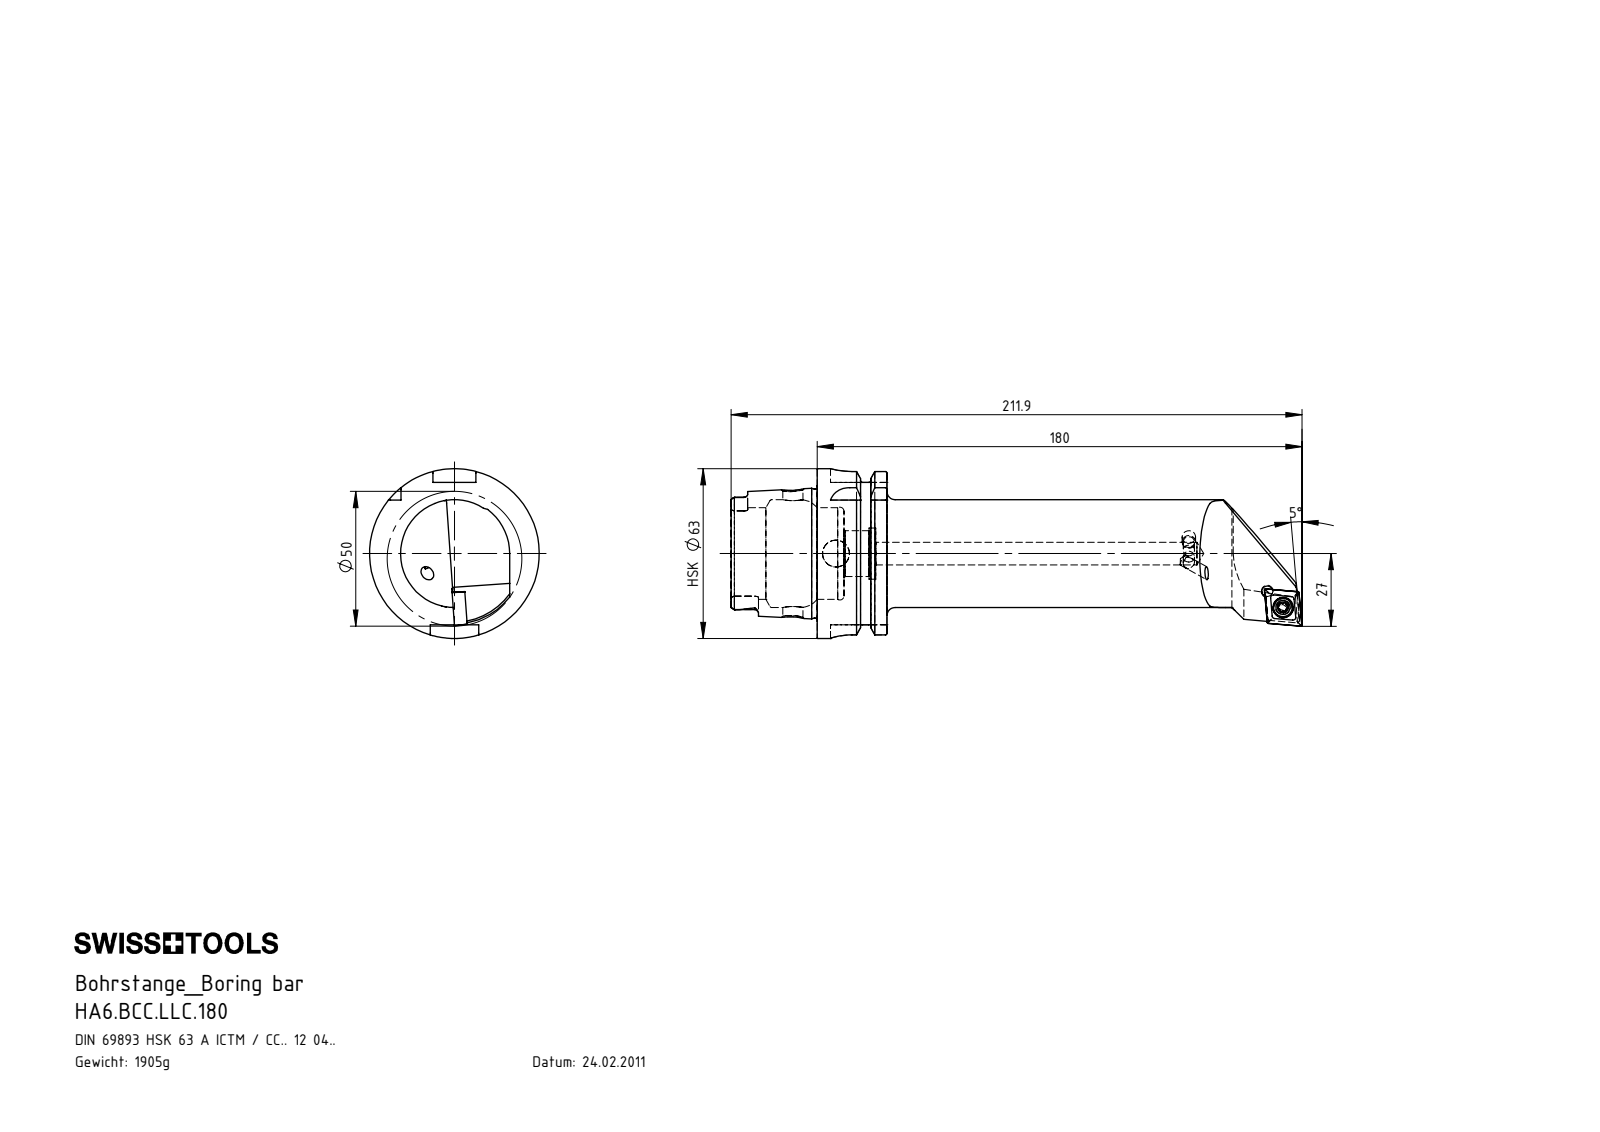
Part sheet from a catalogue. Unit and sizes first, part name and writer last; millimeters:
Units: millimetres
Overall size (bounding box): 211.86 × 63 × 63
Round holes (diameter × count): ⌀4.2 ×4, ⌀4 ×1, ⌀5.5 ×1, ⌀7.5 ×1, ⌀7.6 ×1, ⌀8.4 ×1, ⌀10 ×1, ⌀17 ×1, ⌀19 ×1, ⌀34 ×1, ⌀40 ×1
Round bosses / shafts (diameter × count): ⌀5 ×2, ⌀63 ×1, ⌀54.95 ×1, ⌀47.94 ×1, ⌀7 ×1
Partial cylindrical surfaces — rounded edges, fillets, slot ends (radius × count): R0.39 ×6, R1.4 ×6, R8 ×4, R0.69 ×3, R0.69 ×3, R2.82 ×2, R2.88 ×2, R3 ×1
Main face-to-face distances: 25.95, 16, 9.95, 31.9, 41.85, 57.85, 52.8, 21.8, 11.85, 53.7
Hole centre spacings: 8.21, 8.32
Volume: 245 243 mm³ · Surface area: 44 807 mm²
Bodies: 5 solids, 298 faces (71 planar, 88 cylindrical, 139 other)
Part name (STEP PRODUCT): WCC-ER2.001.010_A; KVT_MB_600_050; HA6.BCC.LLC.180; CCMT120404 (+1 more)
STEP written by: SolidWorks 2017 (AUTOMOTIVE_DESIGN)
